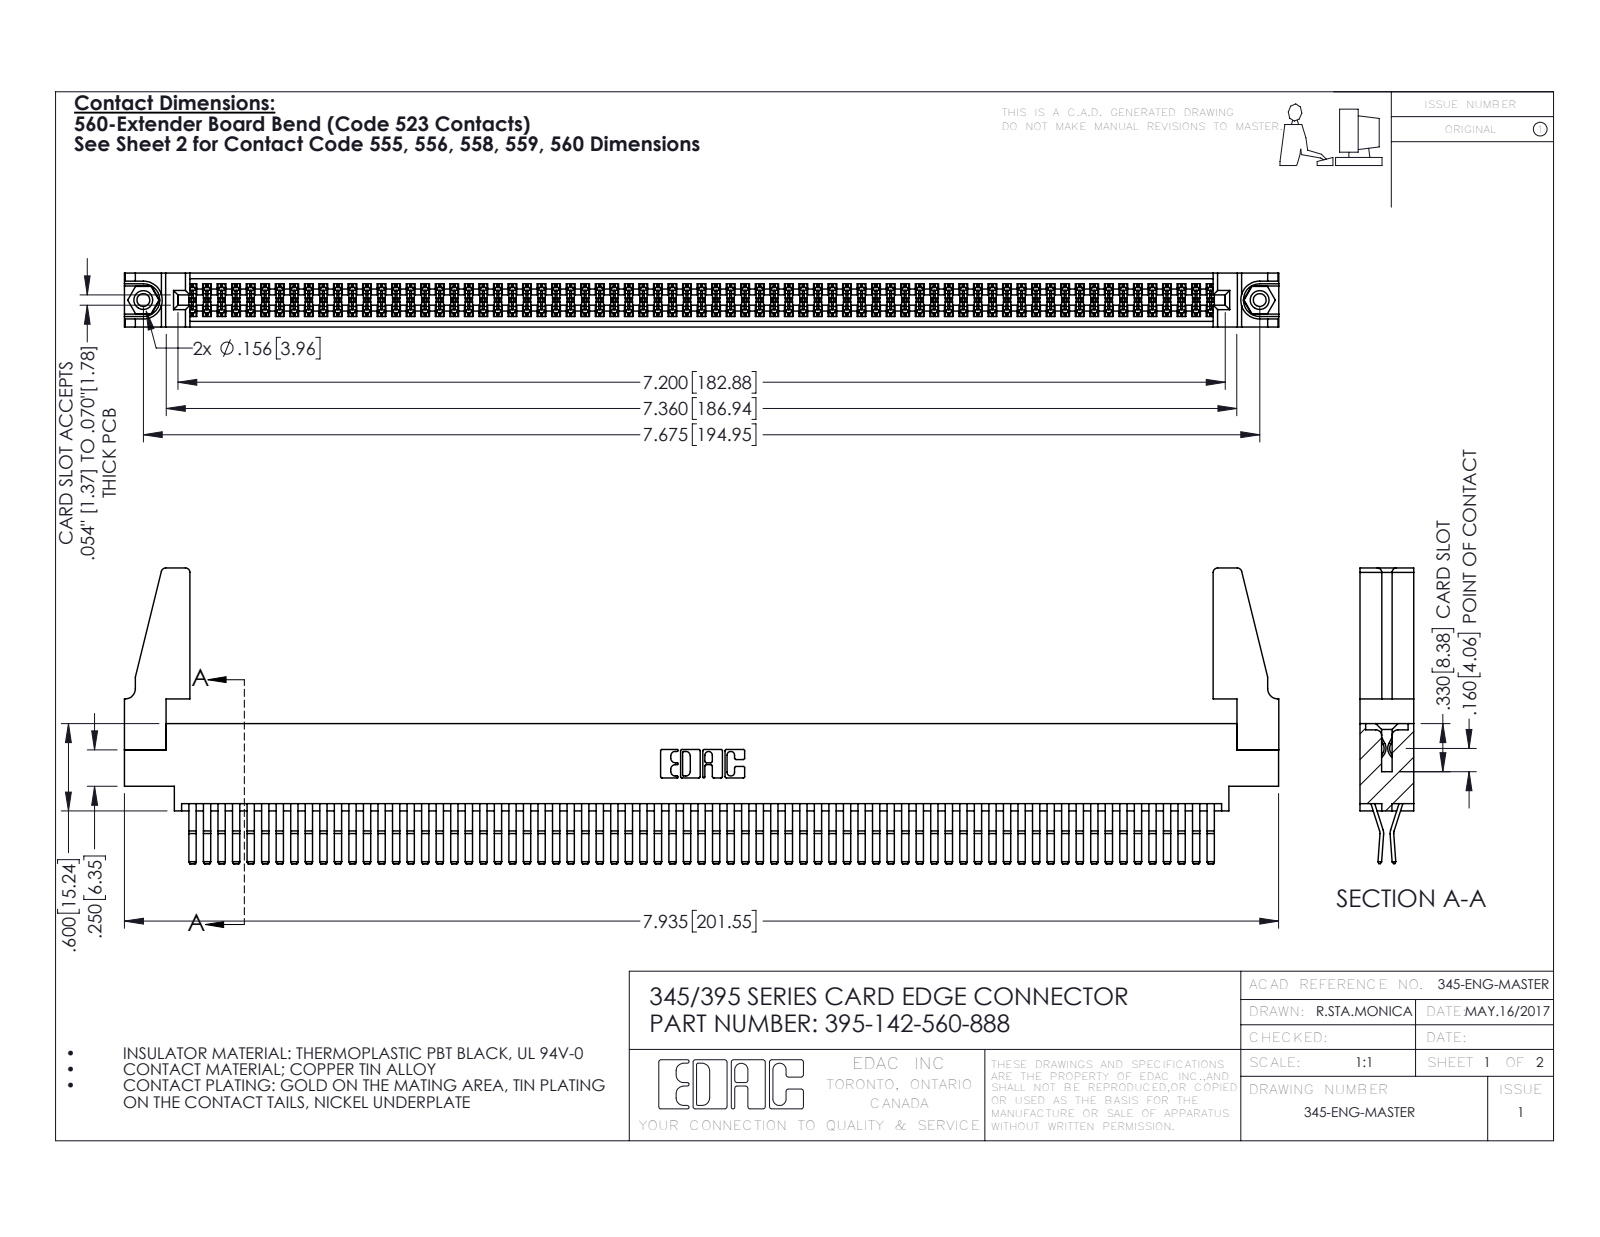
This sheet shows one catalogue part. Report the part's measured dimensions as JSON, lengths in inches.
{"part_name": "395-142-560-888; 345-292-001_560 Tail; 345 Part_0.170 Offset - 0.156 Dia-TH; 345-250-001_345-250-001-102 (+1 more)", "step_written_by": "SolidWorks 2016 (CONFIG_CONTROL_DESIGN)", "units": "inches", "bodies": {"solids": 147, "faces": 7638, "planar": 4842, "cylindrical": 2780, "other": 16}, "overall_size": [7.936, 2.032, 0.37], "volume_in3": 1.46, "surface_area_in2": 57, "round_holes": [[0.089, 2], [0.125, 2], [0.156, 2], [0.064, 1]], "round_bosses_or_shafts": [[0.155, 2]], "partial_cylinders_radius": [[0.006, 214], [0.01, 22], [0.03, 8], [0.007, 6], [0.031, 6], [0.026, 3], [0.01, 2], [0.014, 2]], "face_to_face_distances": [0.072, 0.025, 0.298, 0.37, 0.098, 0.272, 0.2, 0.225, 0.175, 0.149], "hole_center_spacings": [0.27, 7.439, 7.675]}
